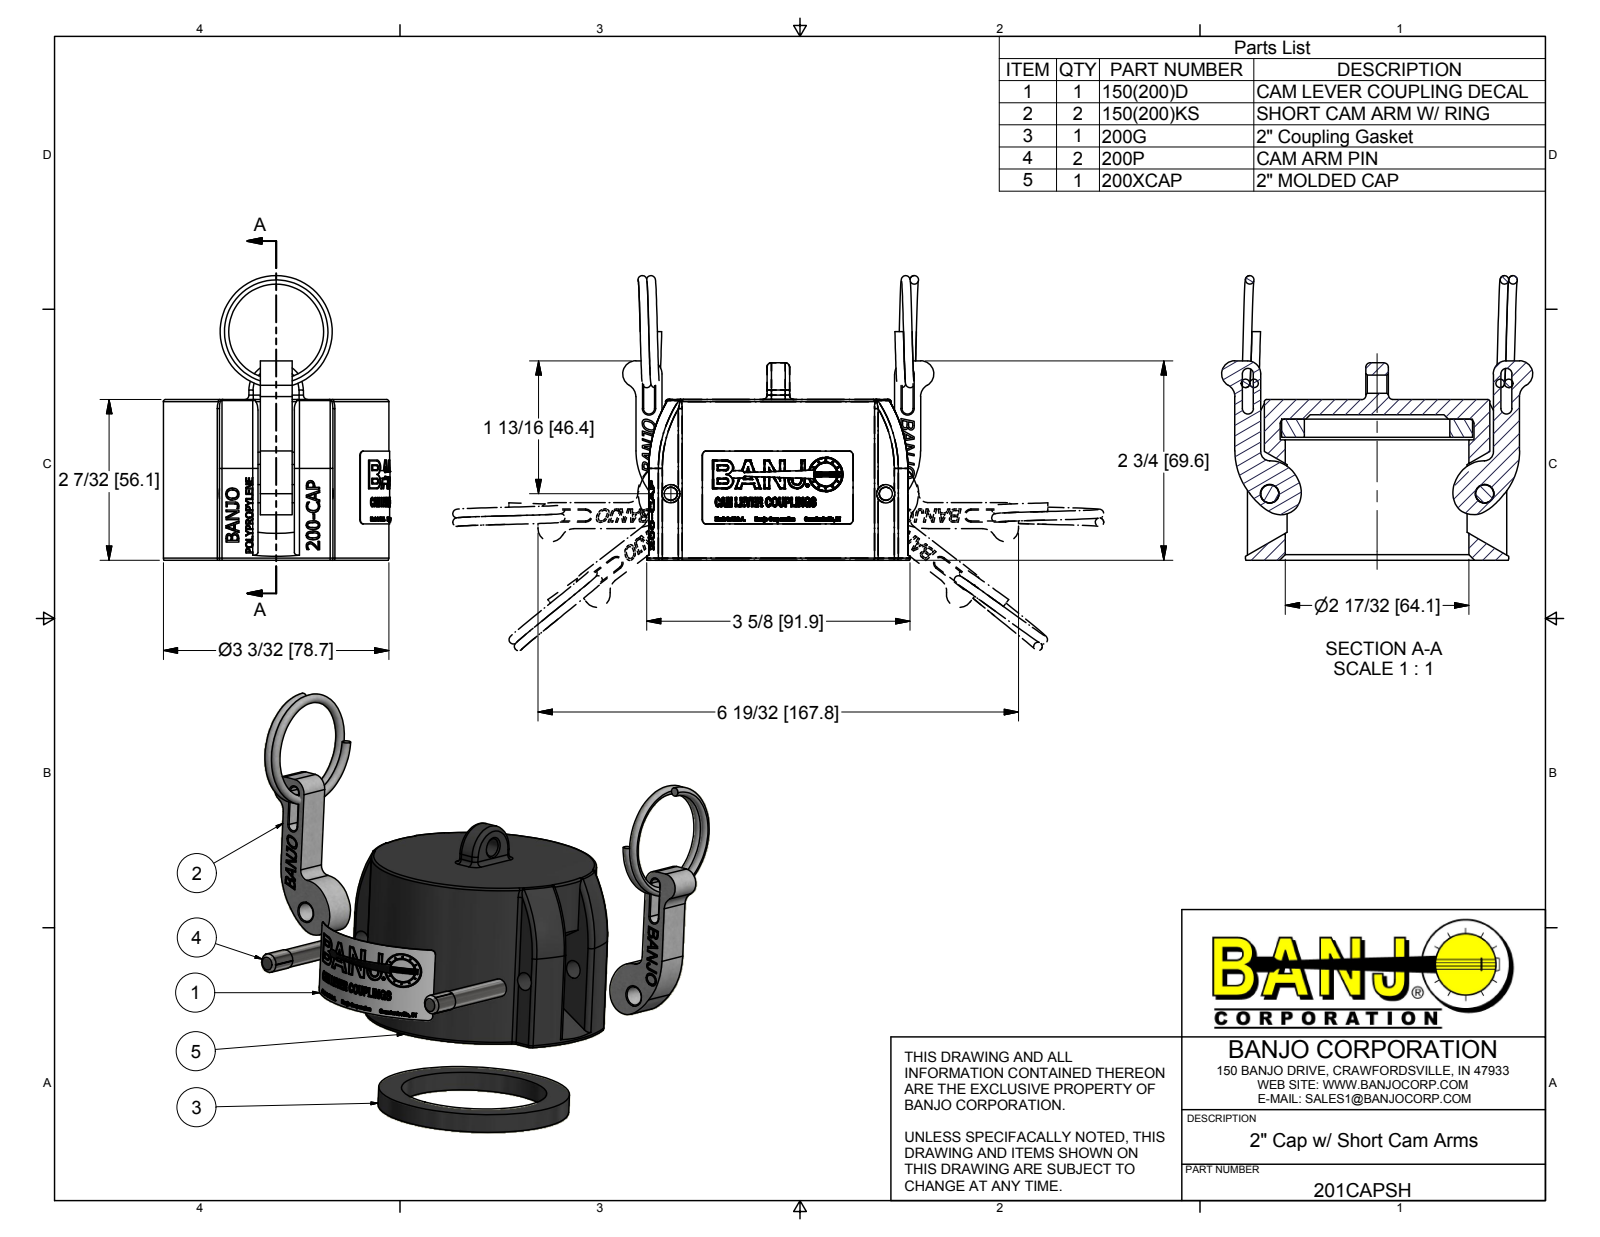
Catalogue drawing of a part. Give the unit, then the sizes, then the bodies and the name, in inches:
Units: inches
Overall size (bounding box): 3.62 × 3.1 × 2.715
Round holes (diameter × count): ⌀0.25 ×3, ⌀2.525 ×1, ⌀2.665 ×1
Partial cylindrical surfaces — rounded edges, fillets, slot ends (radius × count): R0.06 ×22, R0.375 ×1, R1.55 ×1, R1.775 ×1, R1.81 ×1
Main face-to-face distances: 2.21, 0.21, 2, 0.27, 0.06, 1.94, 0.53, 1.03, 0.5, 1.56
Hole centre spacings: 2.955
Volume: 7.397 in³ · Surface area: 59.73 in²
Bodies: 1 solid, 484 faces (169 planar, 79 cylindrical, 236 other)
Part name (STEP PRODUCT): 200XCAP; 201CAPSH
STEP written by: Autodesk Inventor 2016 (AUTOMOTIVE_DESIGN)
